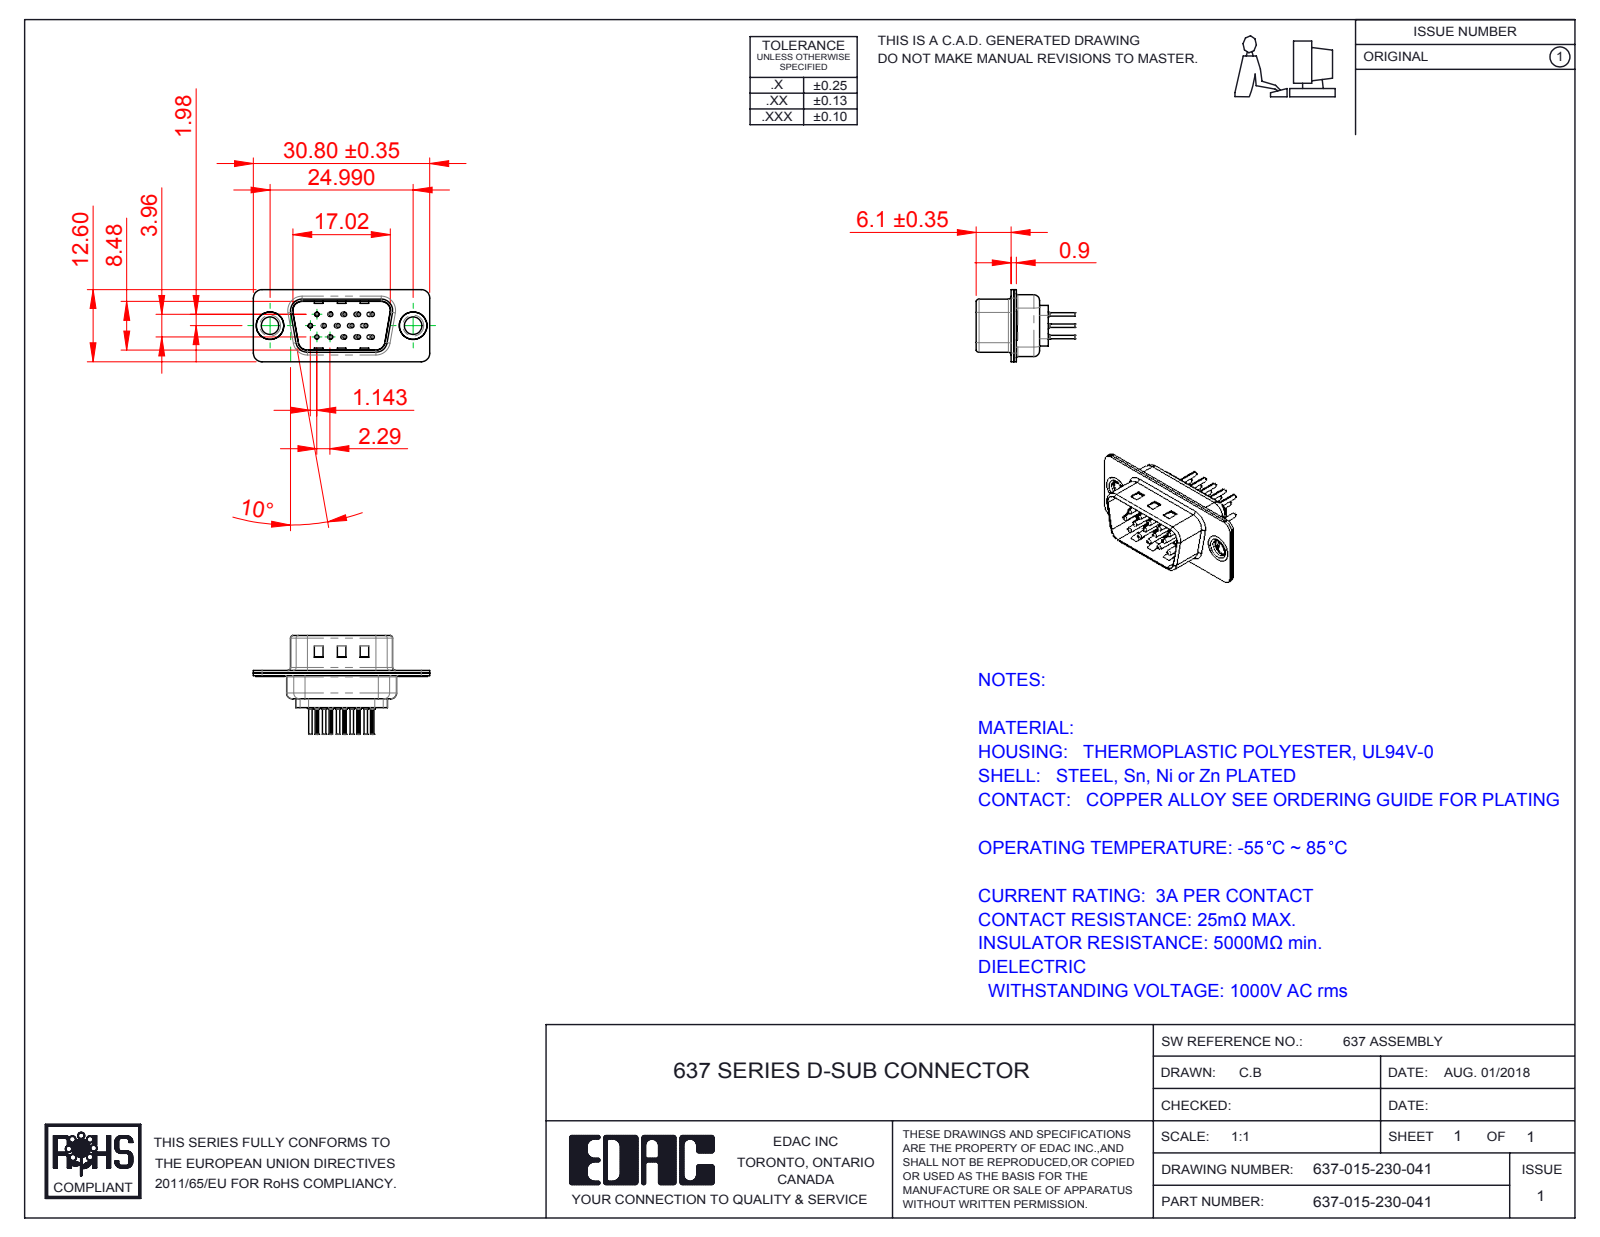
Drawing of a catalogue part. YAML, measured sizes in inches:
part_name: "637 Shell Front_15 Contacts; 637 Housing_15 Contacts; 637-015-230-041; 637 Thru Hole Rivet (+4 more)"
step_written_by: "SolidWorks 2016 (CONFIG_CONTROL_DESIGN)"
units: inches
bodies: {solids: 20, faces: 1778, planar: 467, cylindrical: 668, other: 643}
overall_size: [1.213, 0.679, 0.496]
volume: 0.076
surface_area: 6.977
round_holes:
  - {diameter: 0.063, count: 27}
  - {diameter: 0.008, count: 15}
  - {diameter: 0.014, count: 15}
  - {diameter: 0.043, count: 15}
  - {diameter: 0.03, count: 12}
  - {diameter: 0.079, count: 12}
  - {diameter: 0.12, count: 2}
  - {diameter: 0.157, count: 2}
  - {diameter: 0.189, count: 2}
round_bosses_or_shafts:
  - {diameter: 0.079, count: 15}
  - {diameter: 0.059, count: 15}
  - {diameter: 0.03, count: 15}
  - {diameter: 0.024, count: 15}
  - {diameter: 0.197, count: 2}
  - {diameter: 0.193, count: 2}
  - {diameter: 0.14, count: 2}
partial_cylinders:
  - {radius: 0.004, count: 30}
  - {radius: 0.059, count: 16}
  - {radius: 0.079, count: 12}
  - {radius: 0.02, count: 8}
  - {radius: 0.01, count: 4}
  - {radius: 0.022, count: 4}
  - {radius: 0.028, count: 4}
  - {radius: 0.037, count: 4}
face_to_face_distances: [0.018, 0.035, 0.016, 0.334, 0.028, 0.35, 0.041, 0.012, 0.179, 0.046]
hole_center_spacings: [0.156, 0.09, 0.09, 0.18, 0.095, 0.238, 0.191, 0.093]
